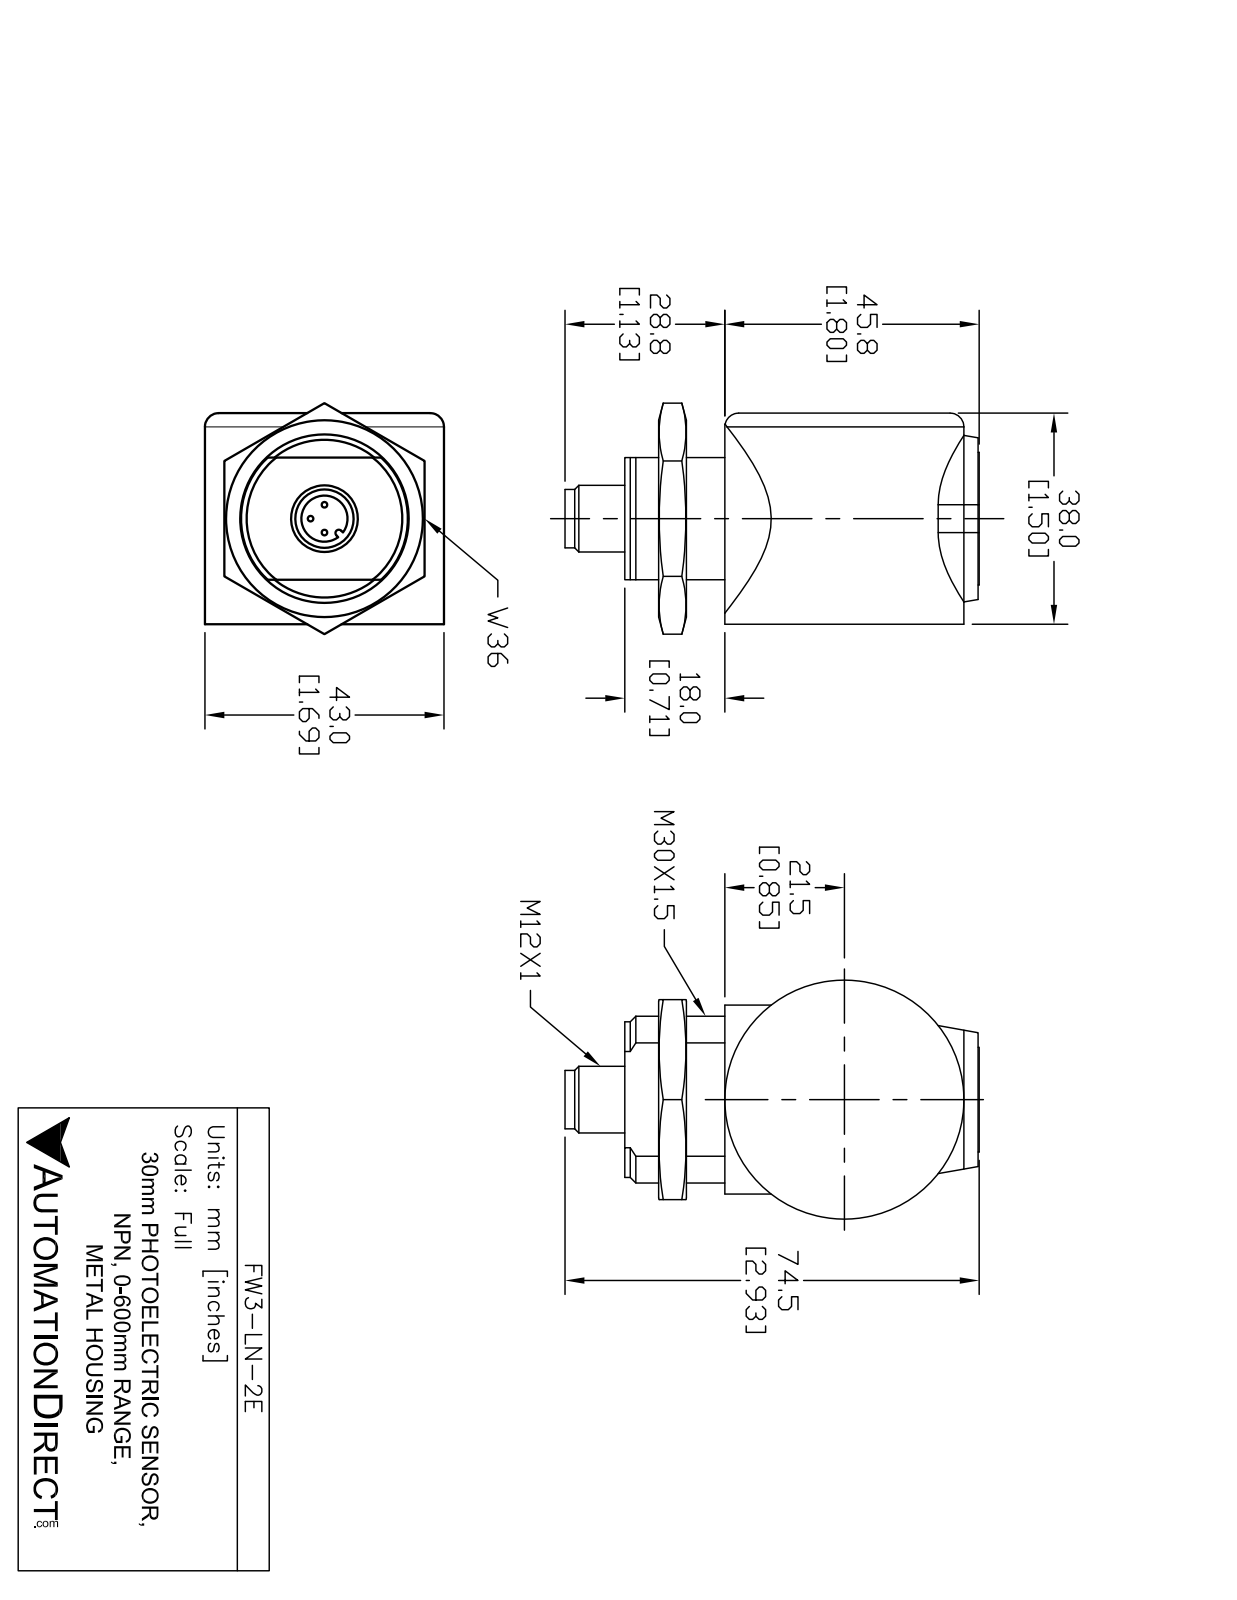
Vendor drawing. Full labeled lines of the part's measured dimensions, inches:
Part name (STEP PRODUCT): FW3-LN-2E
STEP written by: SolidWorks 2013 (AUTOMOTIVE_DESIGN)
Units: inches
Bodies: 1 solid, 201 faces (111 planar, 35 cylindrical, 55 other)
Overall size (bounding box): 2.928 × 1.69 × 1.49
Volume: 4.301 in³ · Surface area: 19.68 in²
Round holes (diameter × count): ⌀0.172 ×1, ⌀0.315 ×1, ⌀1.58 ×1
Round bosses / shafts (diameter × count): ⌀0.04 ×3, ⌀1.69 ×1, ⌀0.47 ×1, ⌀0.39 ×1, ⌀0.18 ×1
Partial cylindrical surfaces — rounded edges, fillets, slot ends (radius × count): R0.48 ×2, R0.64 ×2, R0.025 ×1, R0.408 ×1, R0.492 ×1, R0.545 ×1, R0.587 ×1
Main face-to-face distances: 1.44, 2.498, 0.11, 2.388, 0.3, 0.19, 2.198, 1.178, 0.262, 0.312
Hole centre spacings: 0.349
